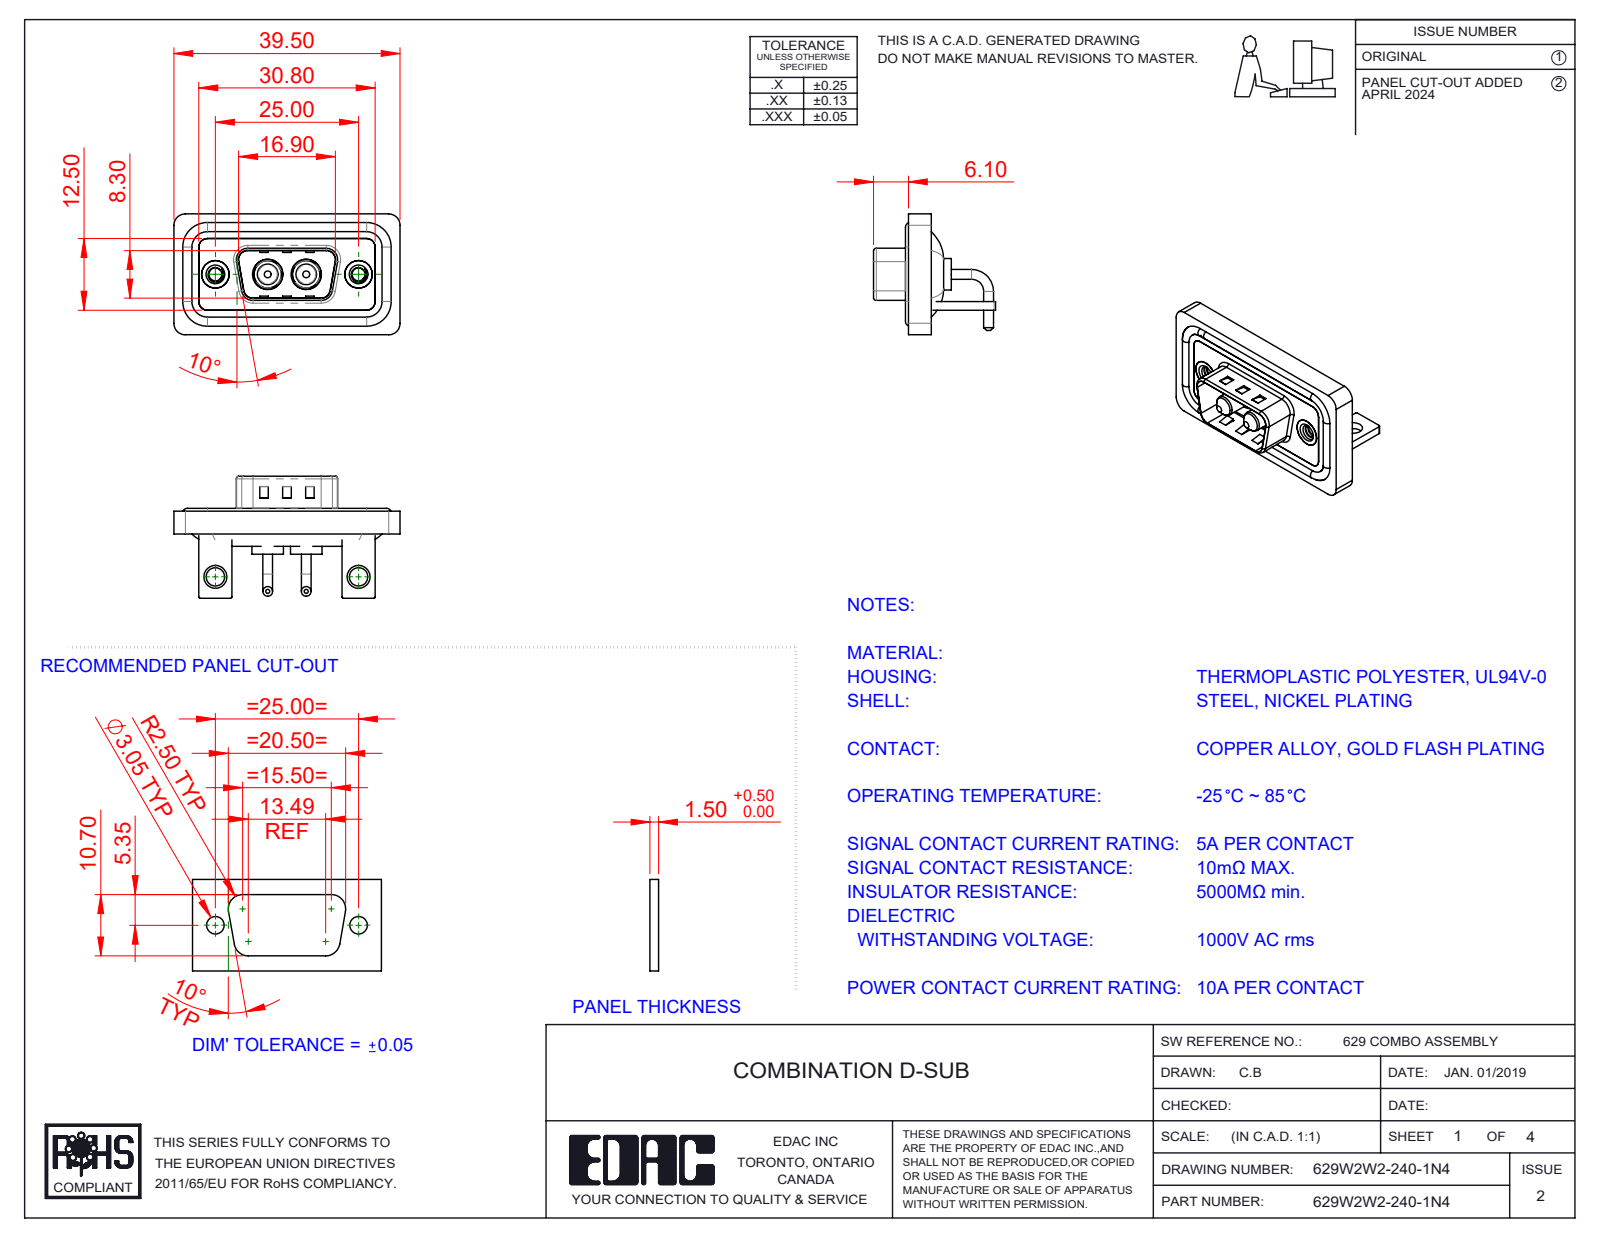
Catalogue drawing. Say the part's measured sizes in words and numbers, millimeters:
The part is named "Power Pin_10A RA; 629W2W2-140-1N4; 629Combo Shell Rear_09 Contacts; 629Combo Stabilizer Bracket (+4 more)". Its 3-D file was written by "SolidWorks 2023 (CONFIG_CONTROL_DESIGN)". It is 13 solids with 537 faces: 185 planar, 240 cylindrical and 112 other. Overall it measures 39.5 by 21.3 by 21.1 millimeters. Its volume is 4 746 cubic millimeters and its surface area 7 652 square millimeters. Round holes: 2 of diameter 2.26, 2 of diameter 3.2, 2 of diameter 4, 2 of diameter 4.8, 2 of diameter 4.85, 2 of diameter 5, 2 of diameter 5.3. Round bosses or shafts: 4 of diameter 1.7, 4 of diameter 1.6, 2 of diameter 5.5, 2 of diameter 5.2, 2 of diameter 4.9, 2 of diameter 4.75, 2 of diameter 3.75, 2 of diameter 3.6. Partial cylindrical surfaces (rounded edges, fillets, slot ends): 19 of radius 2, 18 of radius 1.5, 16 of radius 0.25, 9 of radius 0.5, 8 of radius 1.6, 4 of radius 0.6, 4 of radius 0.65, 4 of radius 0.9. The main face-to-face distances are 0.4, 1.5, 2.9, 0.8, 1.1, 1.2, 2.1, 1.6, 3.7, 2.5. The hole center spacings are 9.14, 15.86, 25, 6.72.
